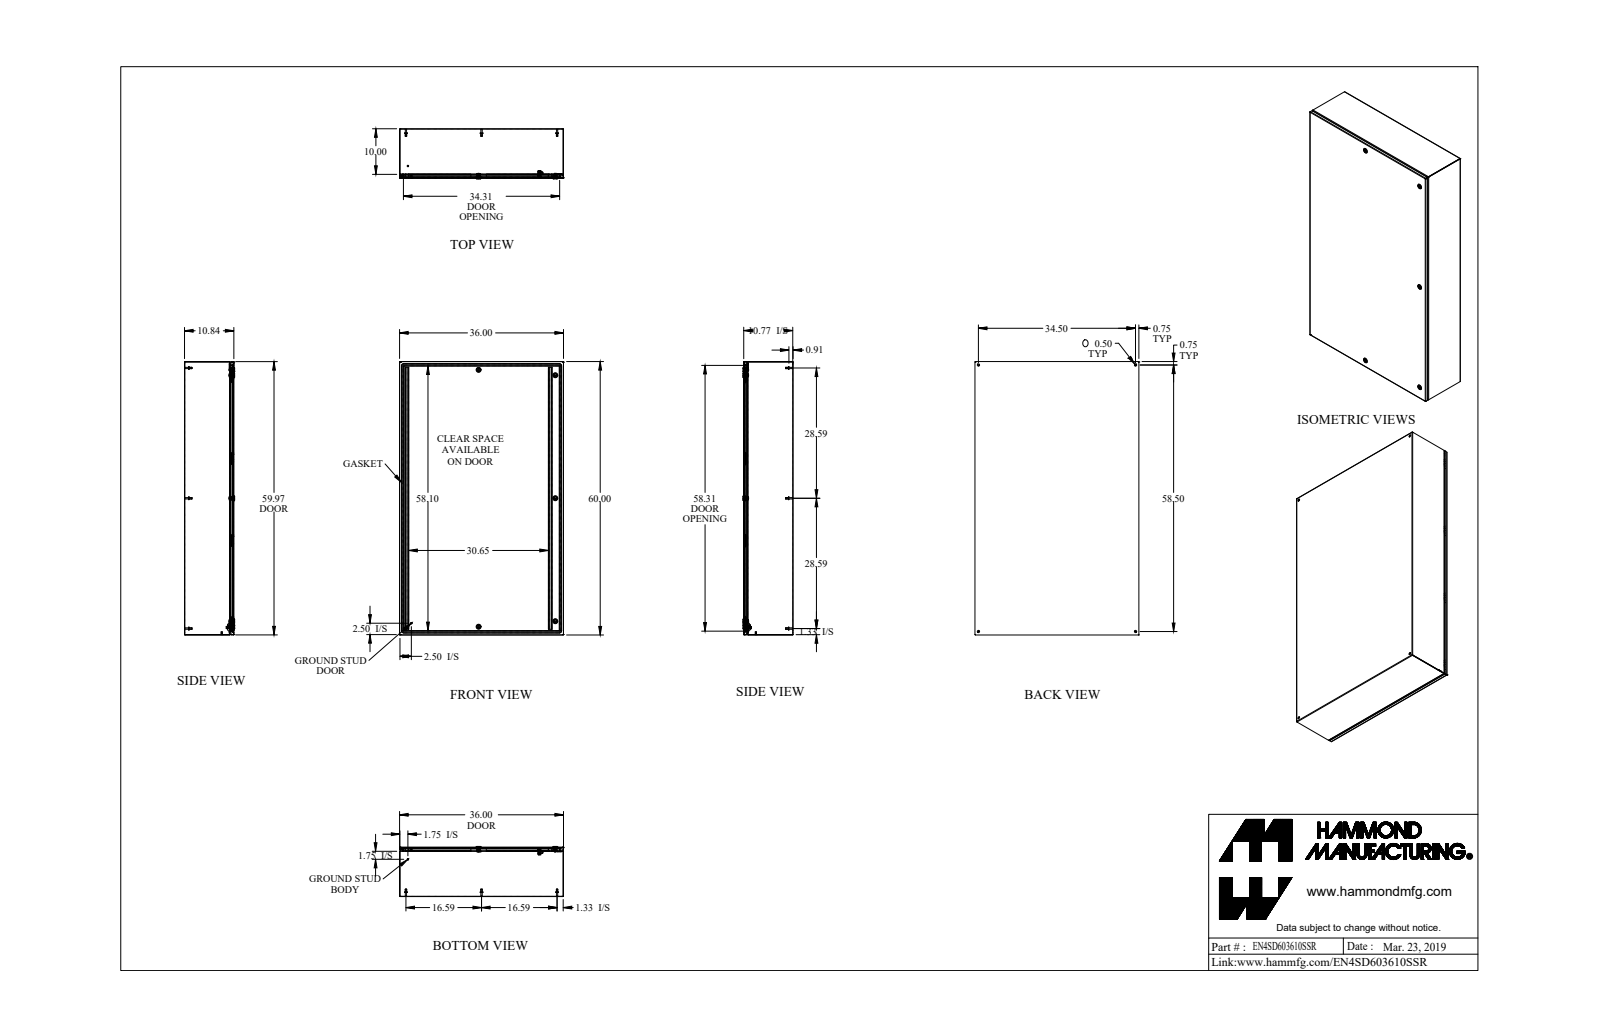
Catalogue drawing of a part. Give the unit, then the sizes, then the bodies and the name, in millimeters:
Units: millimetres
Overall size (bounding box): 1524 × 914.4 × 279.5
Round holes (diameter × count): ⌀12.7 ×9, ⌀5 ×5, ⌀9.8 ×5, ⌀16 ×5, ⌀19.5 ×5, ⌀4.4 ×1, ⌀5 ×1, ⌀6.1 ×1, ⌀6.1 ×1, ⌀7 ×1, ⌀9.5 ×1
Round bosses / shafts (diameter × count): ⌀8 ×10, ⌀15.9 ×9, ⌀7 ×8, ⌀27.9 ×5, ⌀15.9 ×5, ⌀6 ×5, ⌀19.9 ×3, ⌀13.3 ×3
Partial cylindrical surfaces — rounded edges, fillets, slot ends (radius × count): R1.1 ×24, R0.9 ×20, R2.7 ×20, R1.6 ×18, R2.4 ×10, R3.2 ×10, R0.4 ×9, R0.2 ×8
Main face-to-face distances: 1.8, 273.6, 271.7, 275.4, 912.6, 910.7, 914.4, 1.8, 1522.2, 1524
Hole centre spacings: 422.5, 428.8, 455.4, 743.4, 851.3, 876.3, 1128.4, 1465.2
Volume: 8 484 000 mm³ · Surface area: 9 484 000 mm²
Bodies: 64 solids, 1721 faces (896 planar, 548 cylindrical, 277 other)
Part name (STEP PRODUCT): EN4SD603610SSR
STEP written by: SolidWorks 2018 (AUTOMOTIVE_DESIGN)
